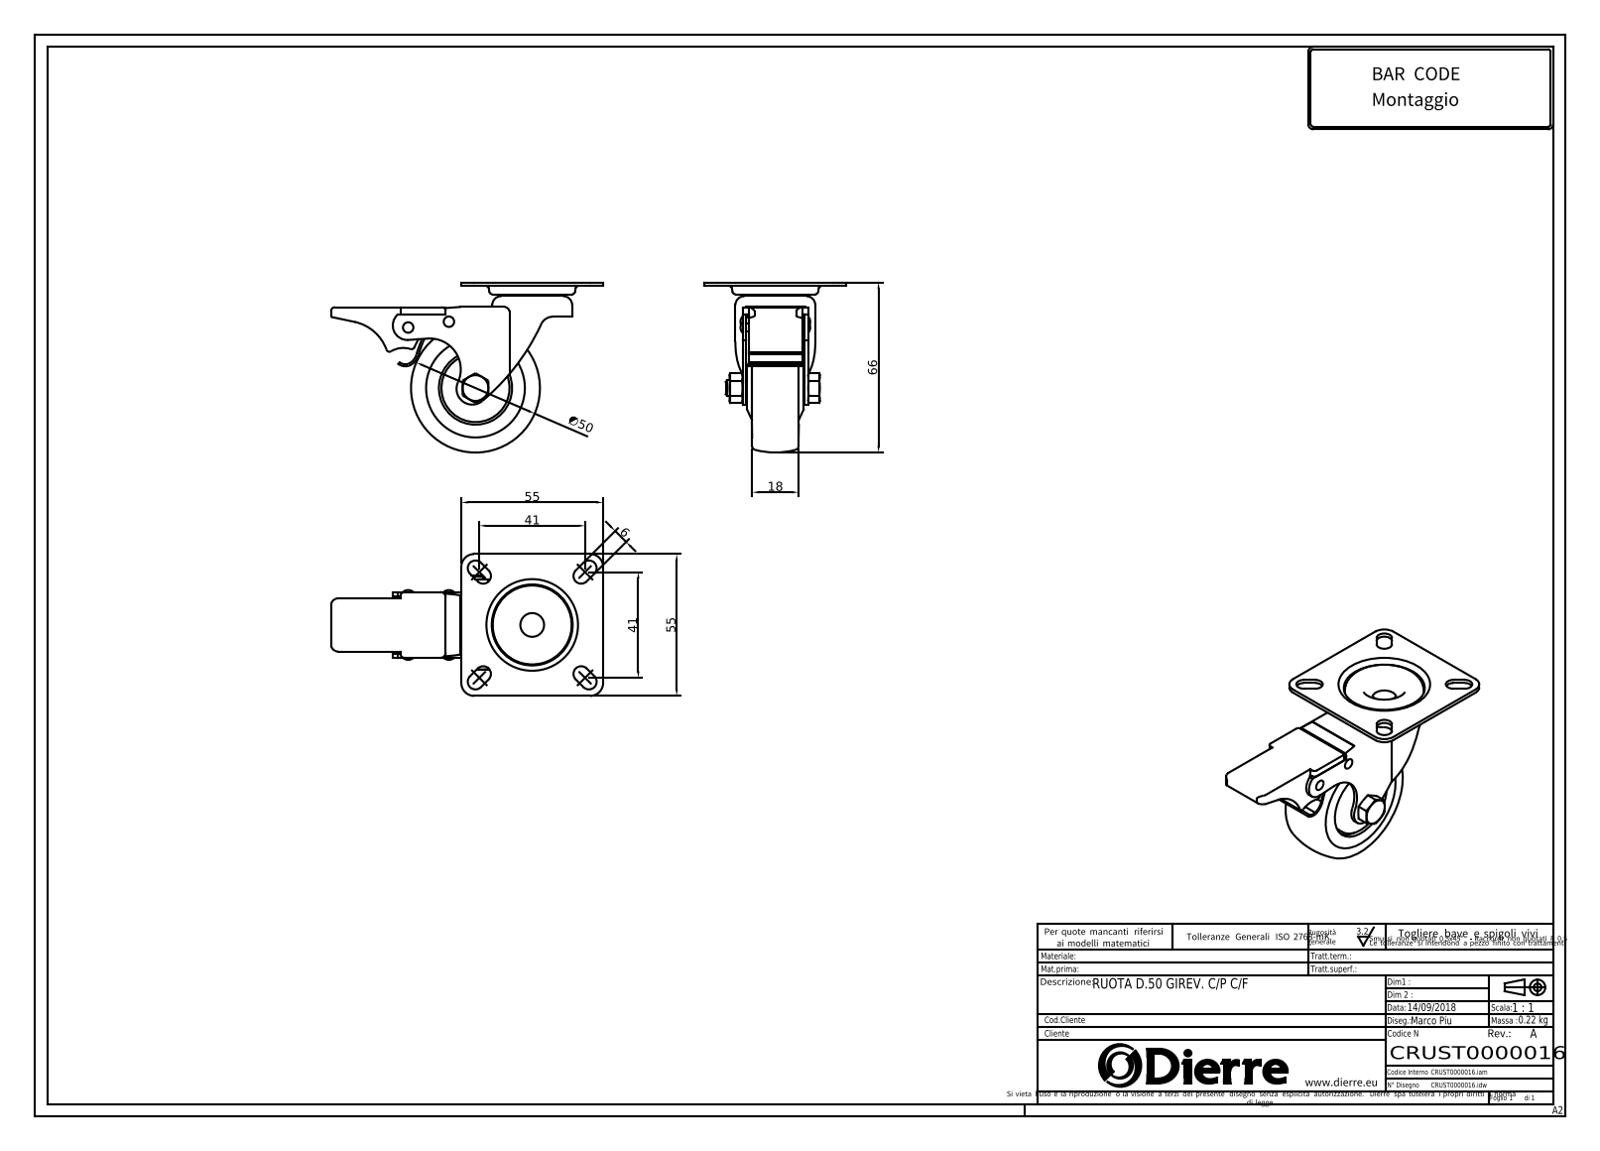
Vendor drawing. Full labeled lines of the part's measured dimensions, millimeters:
Part name (STEP PRODUCT): CRUST0000016; 440000020097; 440000020098; 440000020099 (+4 more)
STEP written by: Autodesk Inventor 2022 (AUTOMOTIVE_DESIGN)
Units: millimetres
Bodies: 8 solids, 243 faces (87 planar, 72 cylindrical, 84 other)
Overall size (bounding box): 105.5 × 66 × 55
Volume: 54 365 mm³ · Surface area: 33 388 mm²
Round holes (diameter × count): ⌀4.92 ×1, ⌀6 ×1, ⌀6.3 ×1, ⌀8 ×1, ⌀9.2 ×1, ⌀16.2 ×1, ⌀25.4 ×1, ⌀28 ×1, ⌀28.4 ×1
Round bosses / shafts (diameter × count): ⌀3 ×2, ⌀31 ×1, ⌀26.4 ×1, ⌀26 ×1, ⌀19 ×1, ⌀7.9 ×1, ⌀5.9 ×1
Partial cylindrical surfaces — rounded edges, fillets, slot ends (radius × count): R3 ×10, R5 ×5, R1.5 ×4, R2 ×4, R0.5 ×2, R87 ×2, R0.6 ×1, R1.2 ×1
Main face-to-face distances: 1.5, 24, 2.25, 21.75, 2.4, 8.18, 9.68, 0.9, 25.5, 23.1
